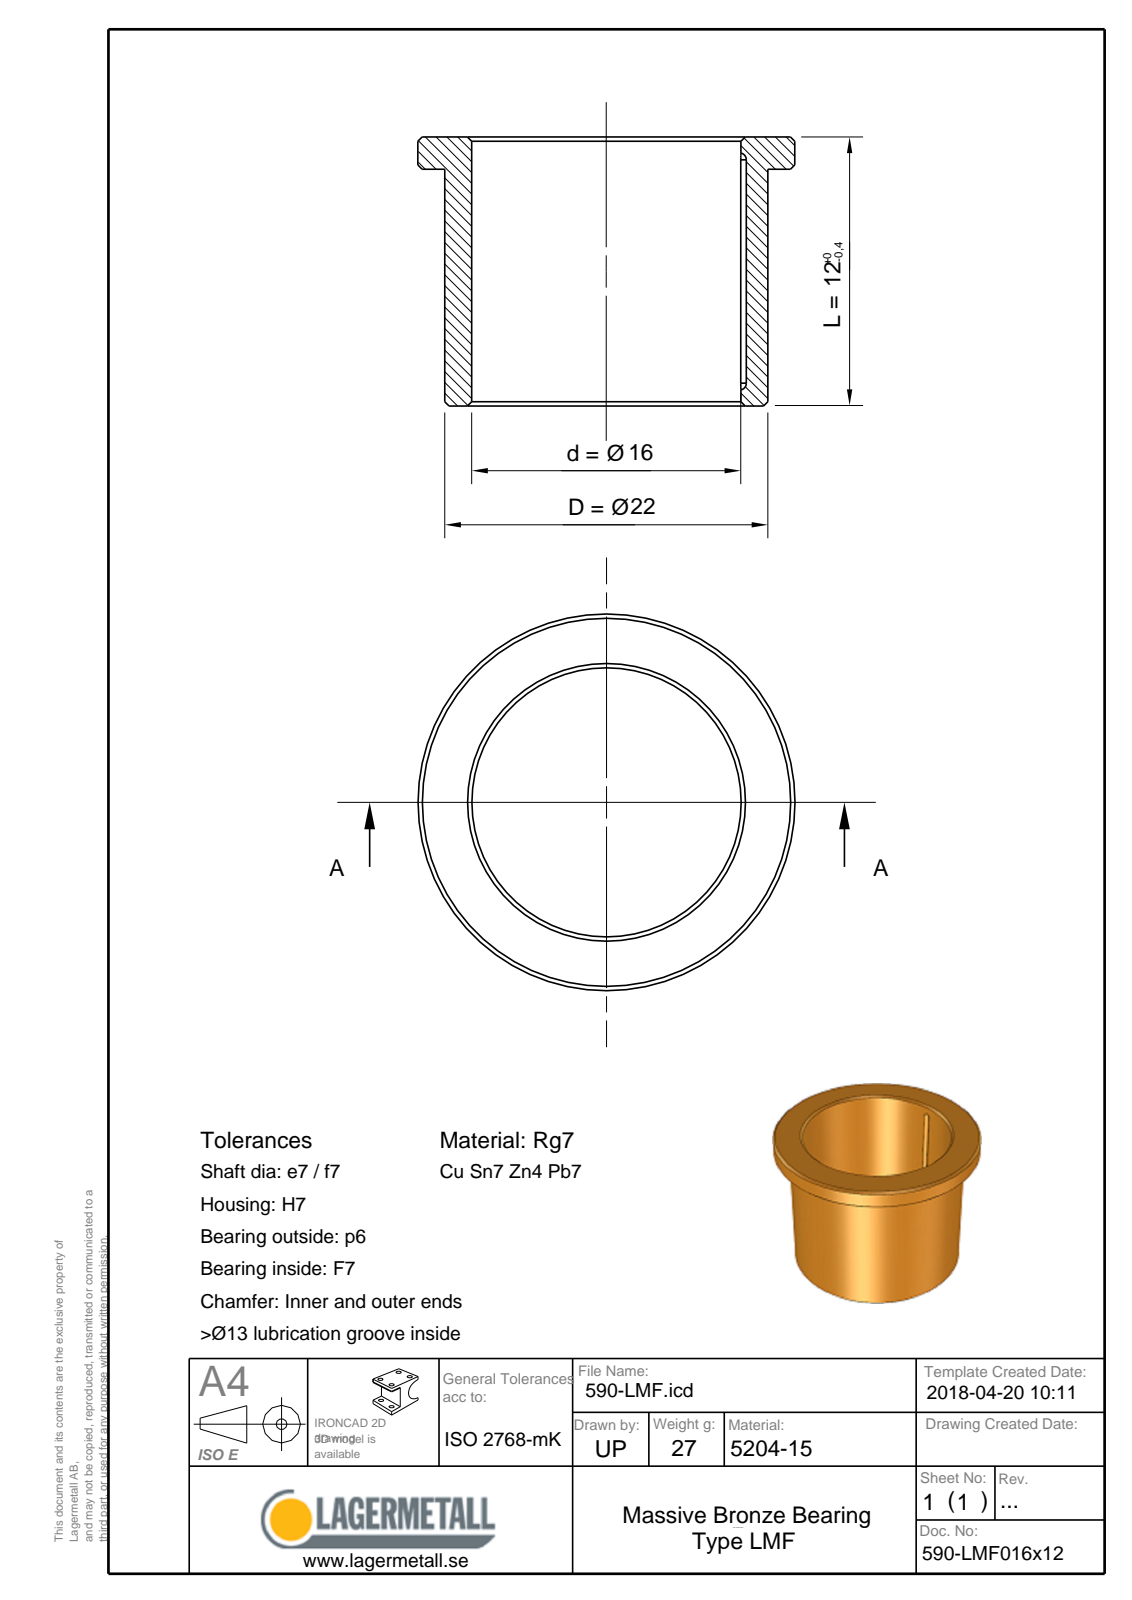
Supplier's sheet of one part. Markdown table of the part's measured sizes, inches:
| quantity | value |
| --- | --- |
| part name | 590-LMF016x12 |
| STEP written by | Spatial InterOp 3D (CONFIG_CONTROL_DESIGN) |
| units | inches |
| bodies | 1 solid, 18 faces (5 planar, 6 cylindrical, 7 other) |
| overall size | 1.102 × 1.102 × 0.472 |
| volume | 0.186 in³ |
| surface area | 3.48 in² |
| round holes (diameter × count) | 0.63 × 1 |
| round bosses / shafts (diameter × count) | 1.102 × 1, 0.866 × 1 |
| partial cylindrical surfaces (radius × count) | 0.03 × 3 |
| main face-to-face distances | 0.157, 0.315, 0.472, 0.059 |
